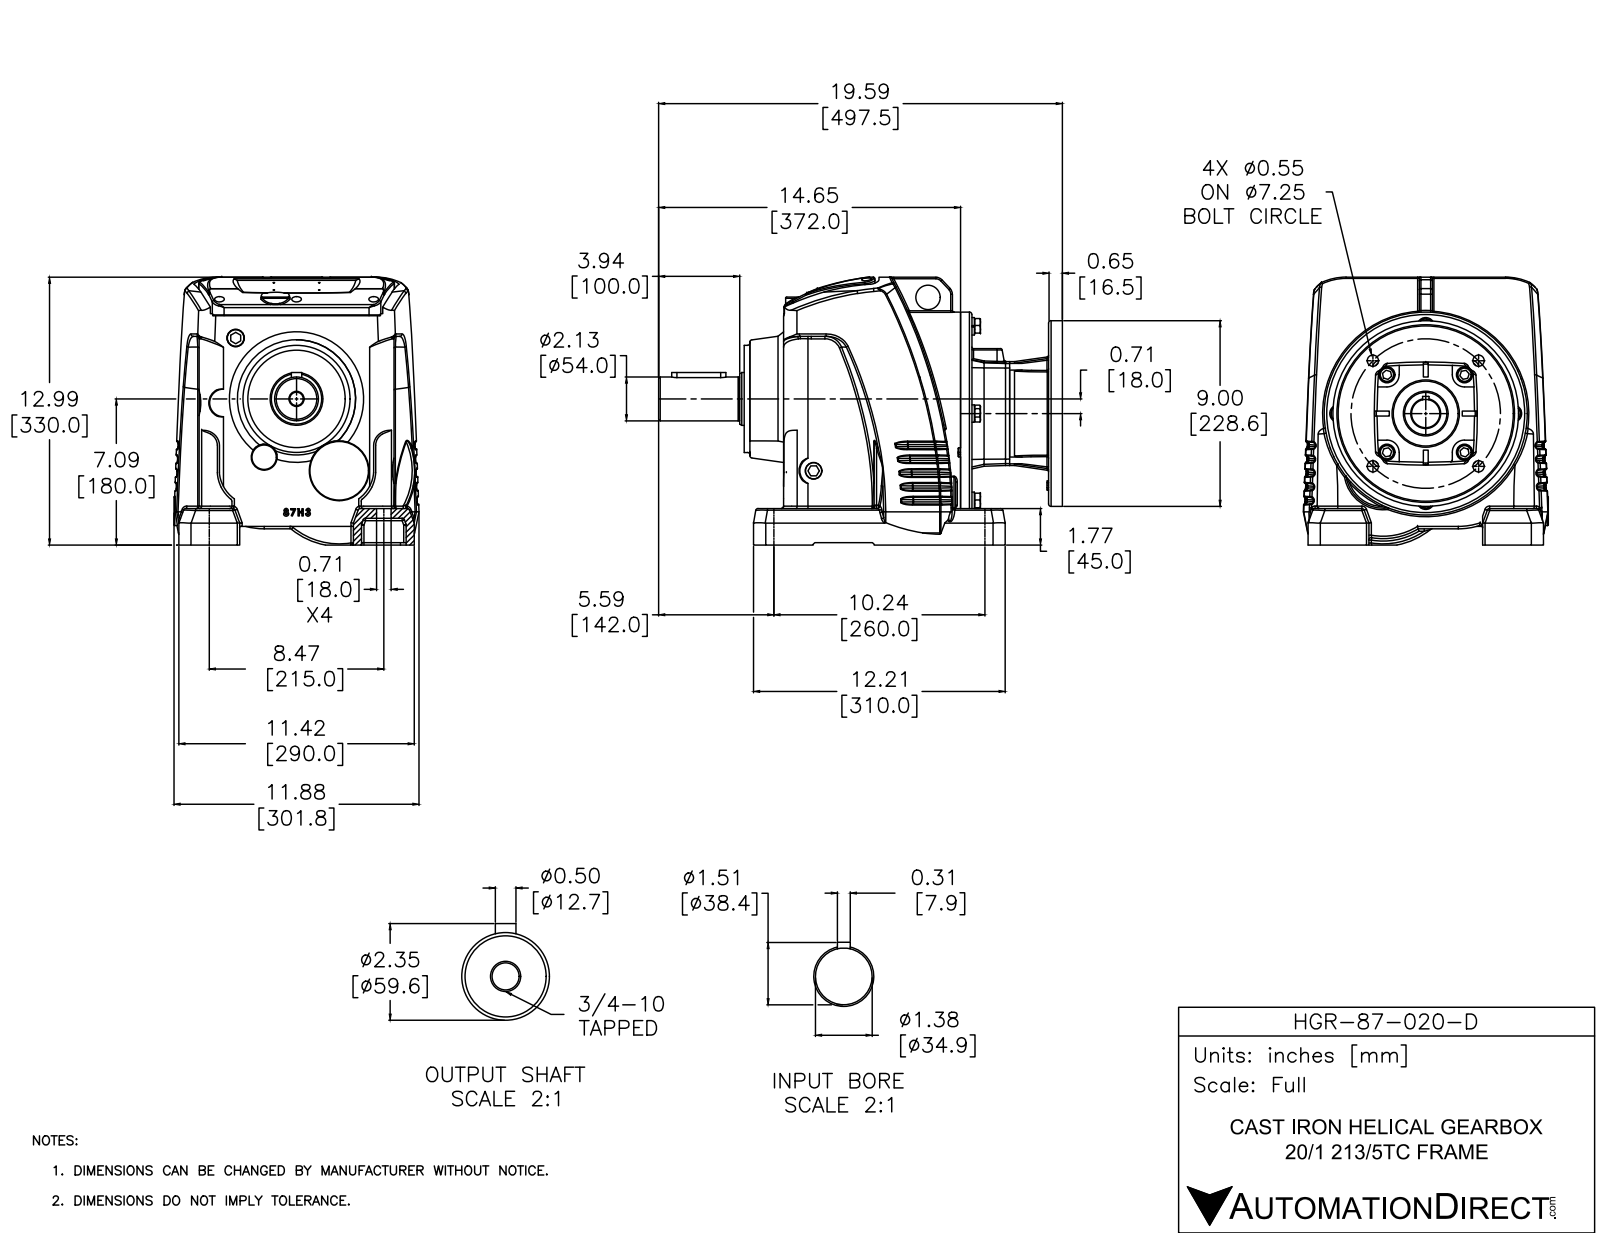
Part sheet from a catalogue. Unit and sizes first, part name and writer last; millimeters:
Units: millimetres
Overall size (bounding box): 497.5 × 330 × 301.8
Round holes (diameter × count): ⌀12 ×7, ⌀2 ×4, ⌀14 ×4, ⌀18 ×4, ⌀20 ×4, ⌀21.3 ×3, ⌀16.7 ×1, ⌀22.3 ×1, ⌀30 ×1, ⌀34.9 ×1, ⌀35 ×1, ⌀55 ×1
Round bosses / shafts (diameter × count): ⌀22 ×5, ⌀21.5 ×4, ⌀18 ×4, ⌀10 ×4, ⌀250 ×1, ⌀228.6 ×1, ⌀139.5 ×1, ⌀132 ×1
Partial cylindrical surfaces — rounded edges, fillets, slot ends (radius × count): R3 ×60, R2 ×18, R15 ×14, R12 ×6, R6 ×4, R10 ×4, R14.5 ×4, R18 ×4
Main face-to-face distances: 215, 1, 14, 15, 232, 10, 65, 243.8, 218, 244.9
Hole centre spacings: 114.2, 24.6, 67.5, 92.1, 95.5, 130.2, 159.6, 73
Volume: 18 760 000 mm³ · Surface area: 991 000 mm²
Bodies: 13 solids, 1385 faces (324 planar, 302 cylindrical, 759 other)
Part name (STEP PRODUCT): HGR-87-015-D
STEP written by: SolidWorks 2015 (CONFIG_CONTROL_DESIGN)
